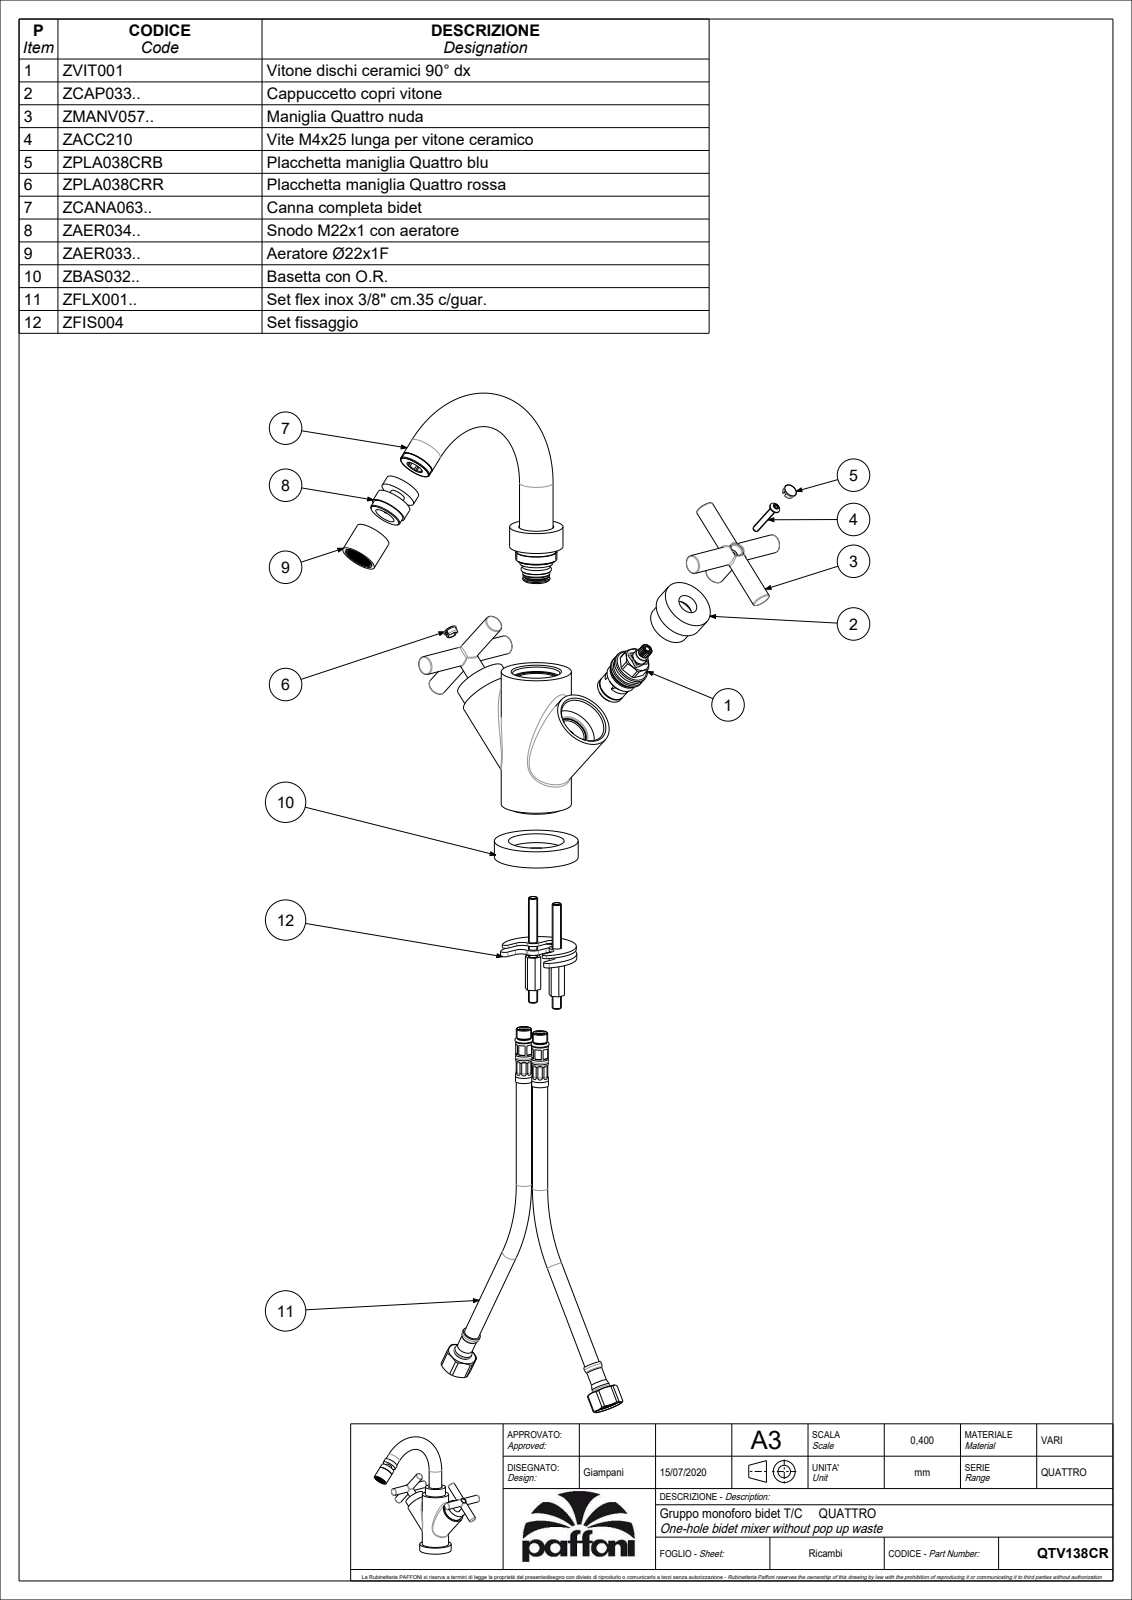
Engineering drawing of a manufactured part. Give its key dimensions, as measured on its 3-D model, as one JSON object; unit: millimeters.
{"part_name": "QTV138CR", "step_written_by": "CREO PARAMETRIC BY PTC INC, 2020044 (CONFIG_CONTROL_DESIGN)", "units": "millimeters", "bodies": {"solids": 5, "faces": 2431, "planar": 1889, "cylindrical": 308, "other": 234}, "overall_size": [215.2, 192.61, 182.56], "volume_mm3": 295524, "surface_area_mm2": 110814, "round_holes": [[9, 6], [19, 4], [7, 3], [3.3, 2], [4.5, 2], [4.6, 2], [8, 2], [8.8, 2], [9.5, 2], [10.3, 2], [11, 2], [13.5, 2]], "round_bosses_or_shafts": [[12, 4], [24, 3], [39, 2], [34, 2], [28, 2], [22, 2], [21.4, 2], [18.6, 2]], "partial_cylinders_radius": [[0.1, 34], [0.5, 4], [1, 4], [3, 2], [9.3, 2], [9.4, 2]], "face_to_face_distances": [5, 4, 12, 13.5, 1, 6, 11, 9, 2, 1.5], "hole_center_spacings": [8.5, 15]}
